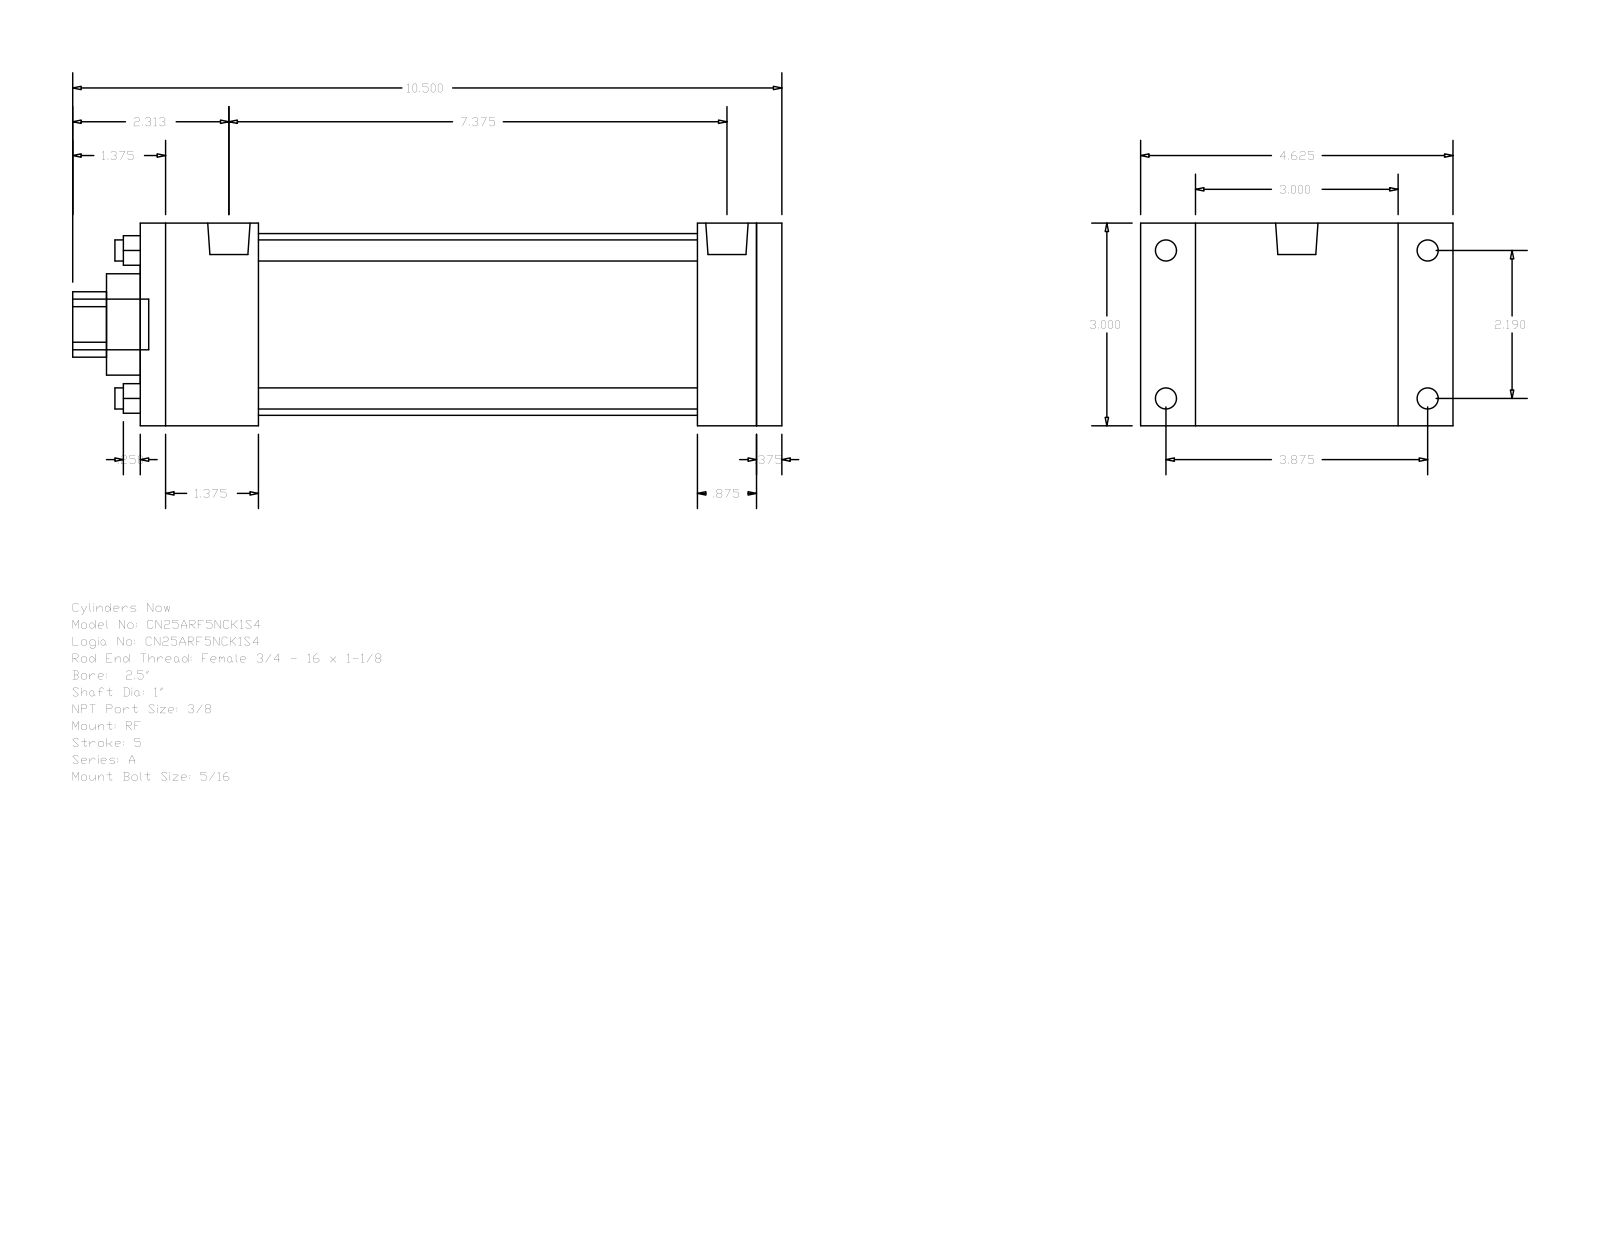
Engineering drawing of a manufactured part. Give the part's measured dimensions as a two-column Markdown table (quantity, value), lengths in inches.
| quantity | value |
| --- | --- |
| part name | A_RF__0250_1 |
| STEP written by | GSSL Pune (CONFIG_CONTROL_DESIGN) |
| units | inches |
| bodies | 0 solids, 92 faces (64 planar, 28 cylindrical, 0 other) |
| overall size | 10.5 × 4.625 × 3 |
| round holes (diameter × count) | 0.313 × 4, 1 × 1, 1.5 × 1, 2.69 × 1 |
| round bosses / shafts (diameter × count) | 0.313 × 4, 0.219 × 4, 0.627 × 2, 0.75 × 1 |
| partial cylindrical surfaces (radius × count) | 0.484 × 1 |
| main face-to-face distances | 3, 9.5, 0.375, 9.125, 1.75, 8.25, 6.5, 7.375, 7.75, 0.875 |
| hole center spacings | 1.548, 2.19, 3.097 |
